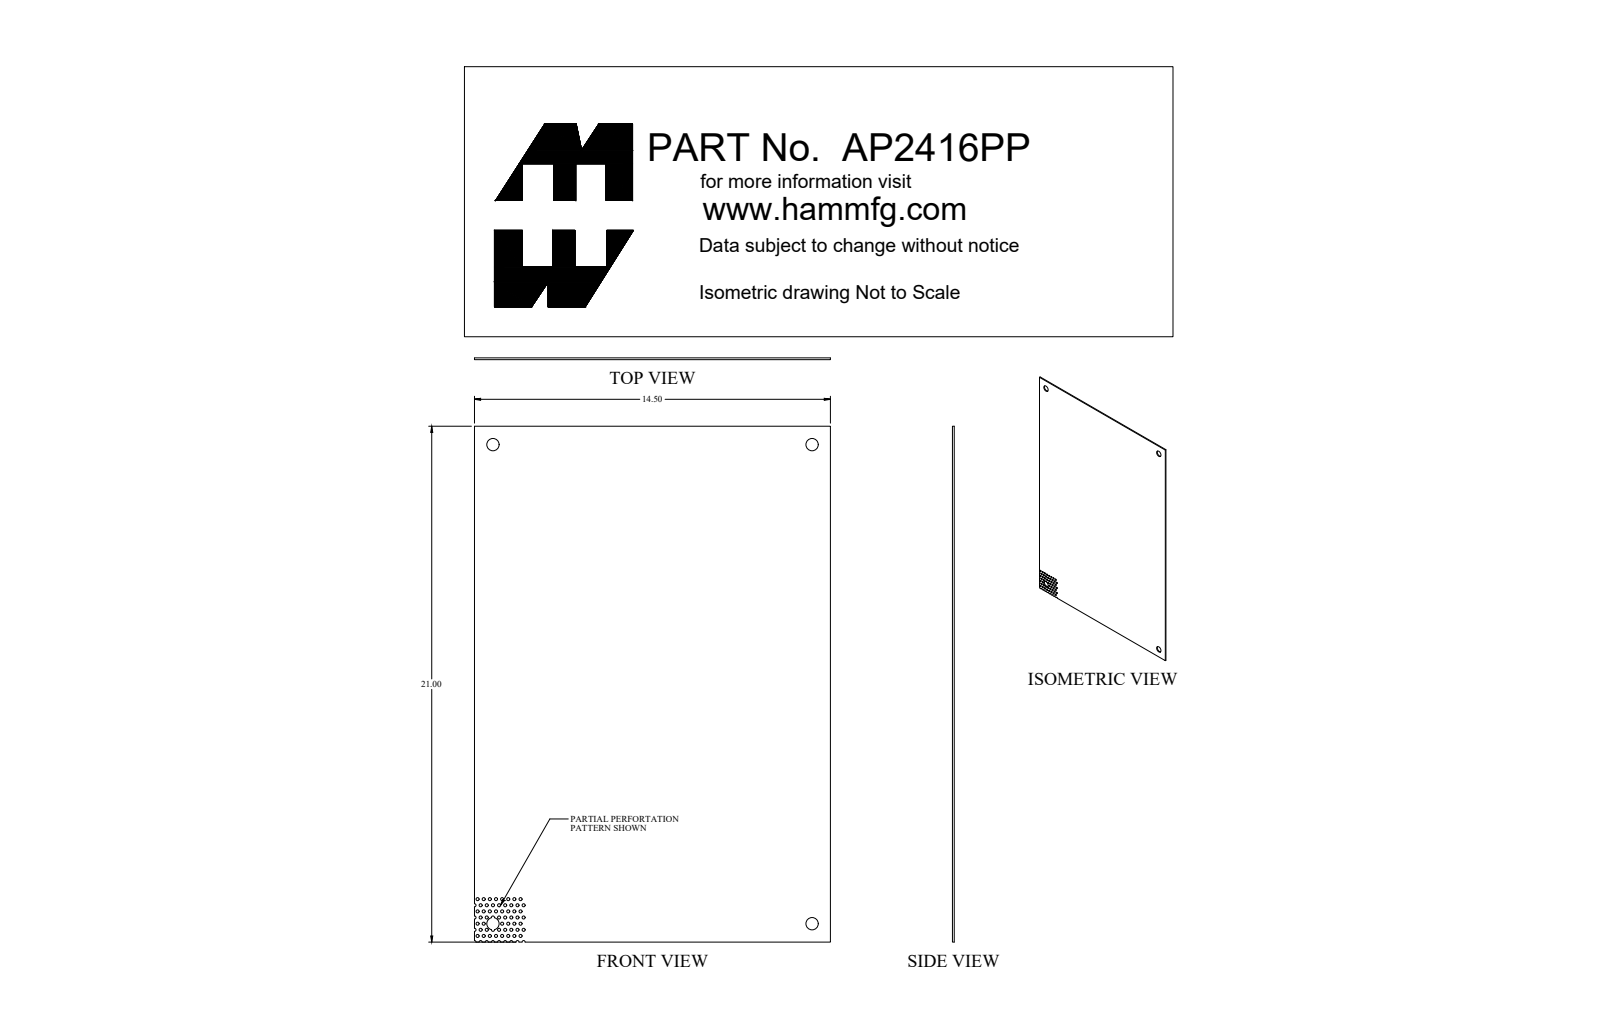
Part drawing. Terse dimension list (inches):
name: AP2416PP_Default
written by: SolidWorks 2019 (CONFIG_CONTROL_DESIGN)
unit: in
bodies: 1 solid, 152 faces (17 planar, 135 cylindrical, 0 other)
size: 21 × 14.5 × 0.072
volume: 21.82 in³; area: 613.1 in²
holes: 37× ⌀0.125, 15× ⌀0.125, 4× ⌀0.5
rounds: 11× R0.063, 3× R0.062
face distances: 0.072, 14.5, 21
hole spacings: 0.28, 0.5, 0.25, 0.45, 0.559, 0.673, 1.152, 0.91
